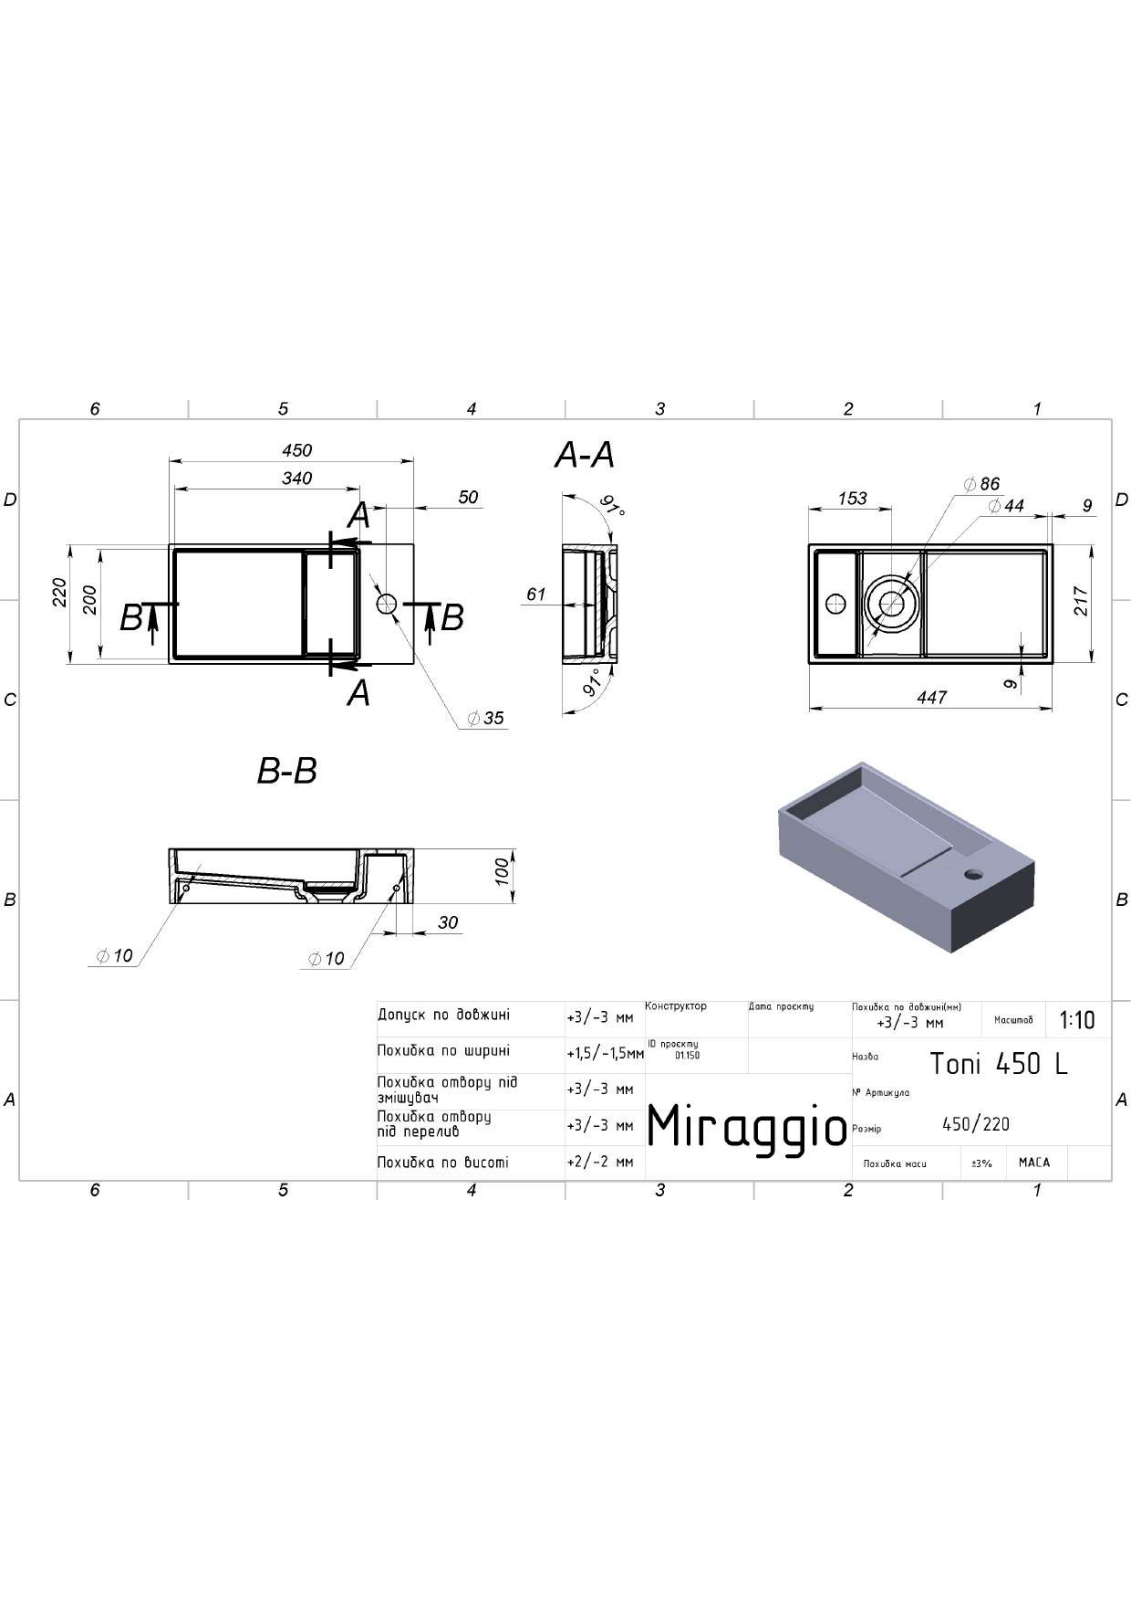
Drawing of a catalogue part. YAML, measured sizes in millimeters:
part_name: "Toni 450 L"
step_written_by: "SolidWorks 2020 (AUTOMOTIVE_DESIGN)"
units: millimeters
bodies: {solids: 2, faces: 122, planar: 30, cylindrical: 42, other: 50}
overall_size: [450, 220, 100]
volume: 2594000
surface_area: 499810
round_holes:
  - {diameter: 10, count: 2}
  - {diameter: 35, count: 1}
  - {diameter: 45, count: 1}
partial_cylinders:
  - {radius: 2, count: 16}
  - {radius: 6, count: 12}
  - {radius: 4, count: 6}
  - {radius: 3, count: 4}
face_to_face_distances: [10, 61, 71, 29, 100, 39, 90, 51, 233.49, 88]
hole_center_spacings: [103.14, 386.5]
